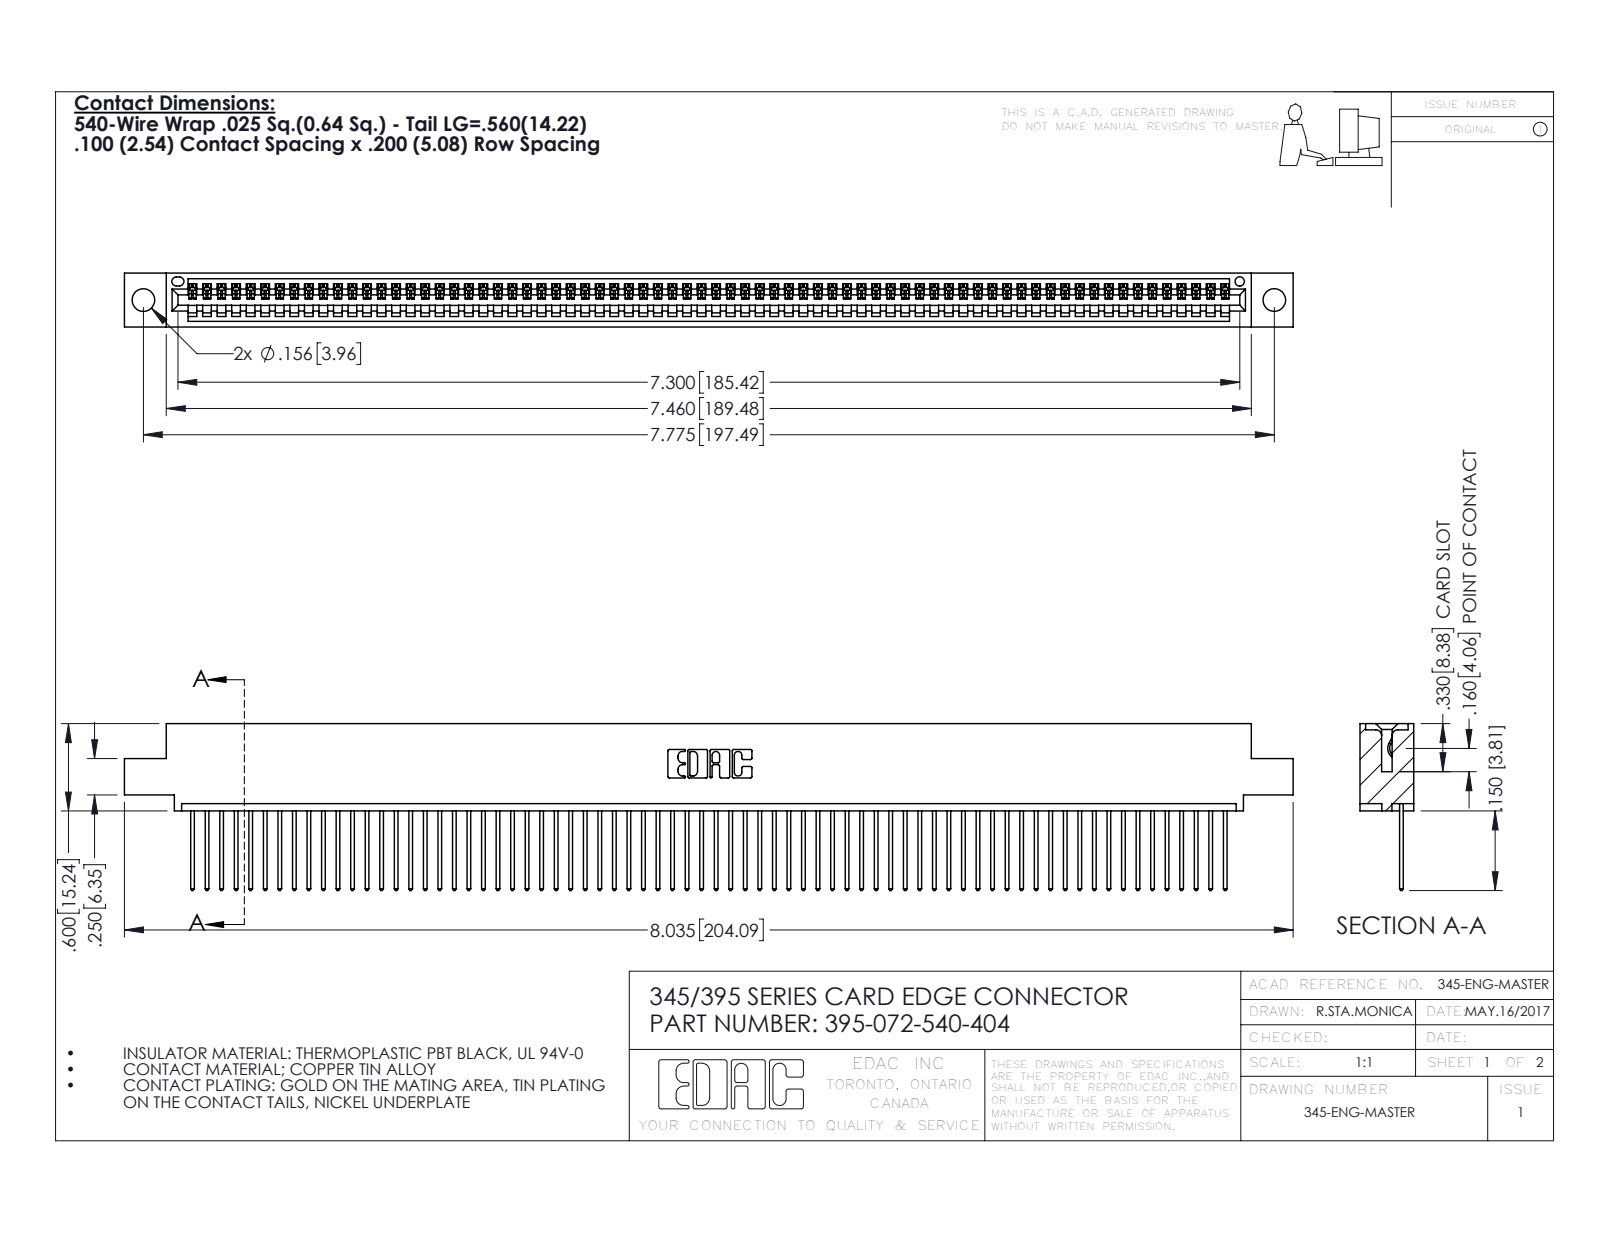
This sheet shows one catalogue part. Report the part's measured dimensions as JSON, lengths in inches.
{"part_name": "345 Part_0.110 Offset - 0.156 Dia-TH; 395-072-540-404; 345-292-001_345-293-140", "step_written_by": "SolidWorks 2016 (CONFIG_CONTROL_DESIGN)", "units": "inches", "bodies": {"solids": 73, "faces": 4306, "planar": 2964, "cylindrical": 1342, "other": 0}, "overall_size": [8.035, 1.147, 0.37], "volume_in3": 1.194, "surface_area_in2": 41.85, "round_holes": [[0.156, 2], [0.064, 1]], "partial_cylinders_radius": [[0.006, 144], [0.01, 144], [0.01, 22], [0.007, 6], [0.031, 6], [0.026, 3], [0.031, 2], [0.04, 2]], "face_to_face_distances": [0.072, 0.298, 0.37, 0.098, 0.272, 0.025, 0.2, 0.225, 0.149, 0.072], "hole_center_spacings": [0.27, 7.539, 7.775]}
